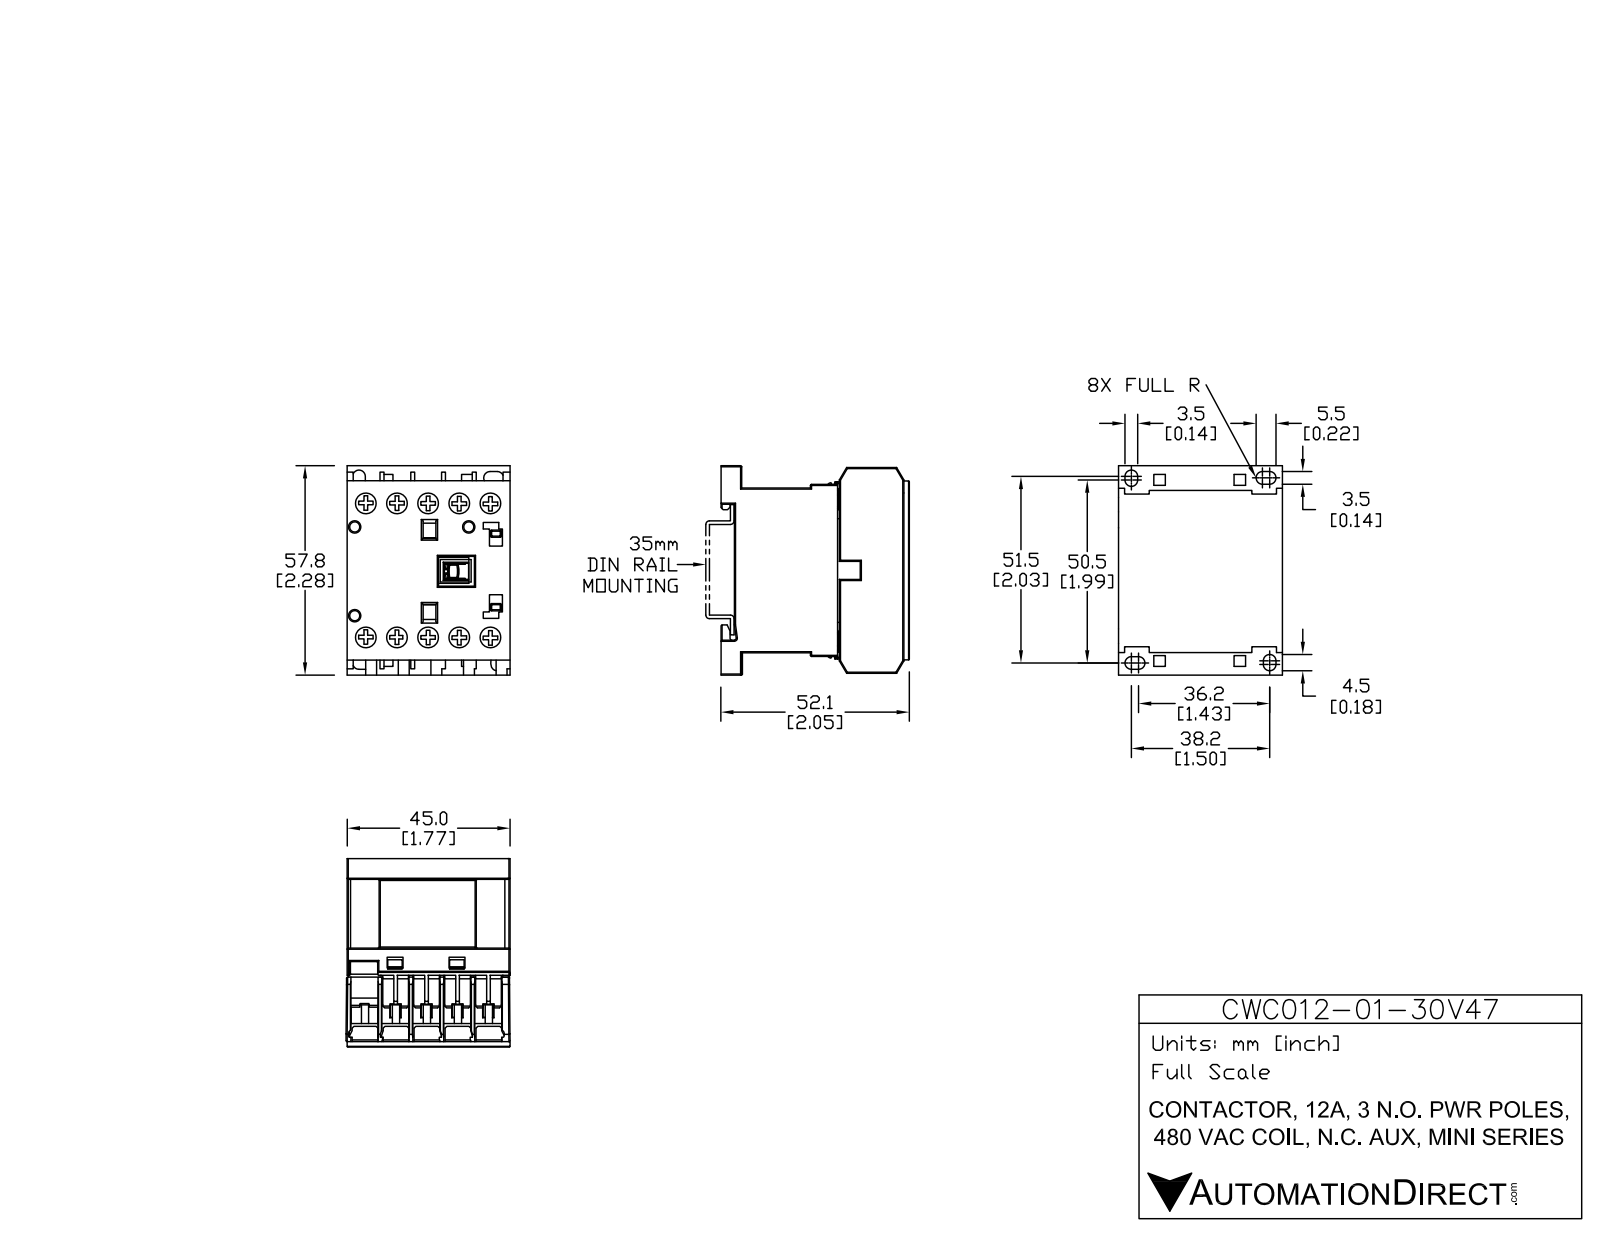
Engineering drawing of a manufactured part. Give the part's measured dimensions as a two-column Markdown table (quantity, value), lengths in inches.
| quantity | value |
| --- | --- |
| part name | CWC12-01-30V47 |
| STEP written by | SolidWorks 2013 (AUTOMOTIVE_DESIGN) |
| units | inches |
| bodies | 15 solids, 535 faces (445 planar, 90 cylindrical, 0 other) |
| overall size | 2.285 × 2.052 × 1.801 |
| volume | 5.927 in³ |
| surface area | 47.18 in² |
| round holes (diameter × count) | 0.244 × 10, 0.11 × 3 |
| round bosses / shafts (diameter × count) | 0.232 × 10 |
| partial cylindrical surfaces (radius × count) | 0.012 × 20, 0.068 × 6, 0.068 × 2, 0.013 × 1, 0.017 × 1, 0.022 × 1 |
| main face-to-face distances | 0.325, 1.791, 0.049, 0.65, 0.374, 0.217, 0.699, 0.202, 0.419, 0.276 |
| hole center spacings | 0.337, 1.494, 0.673, 1.603, 1.455, 1.01, 1.771, 0.272 |
